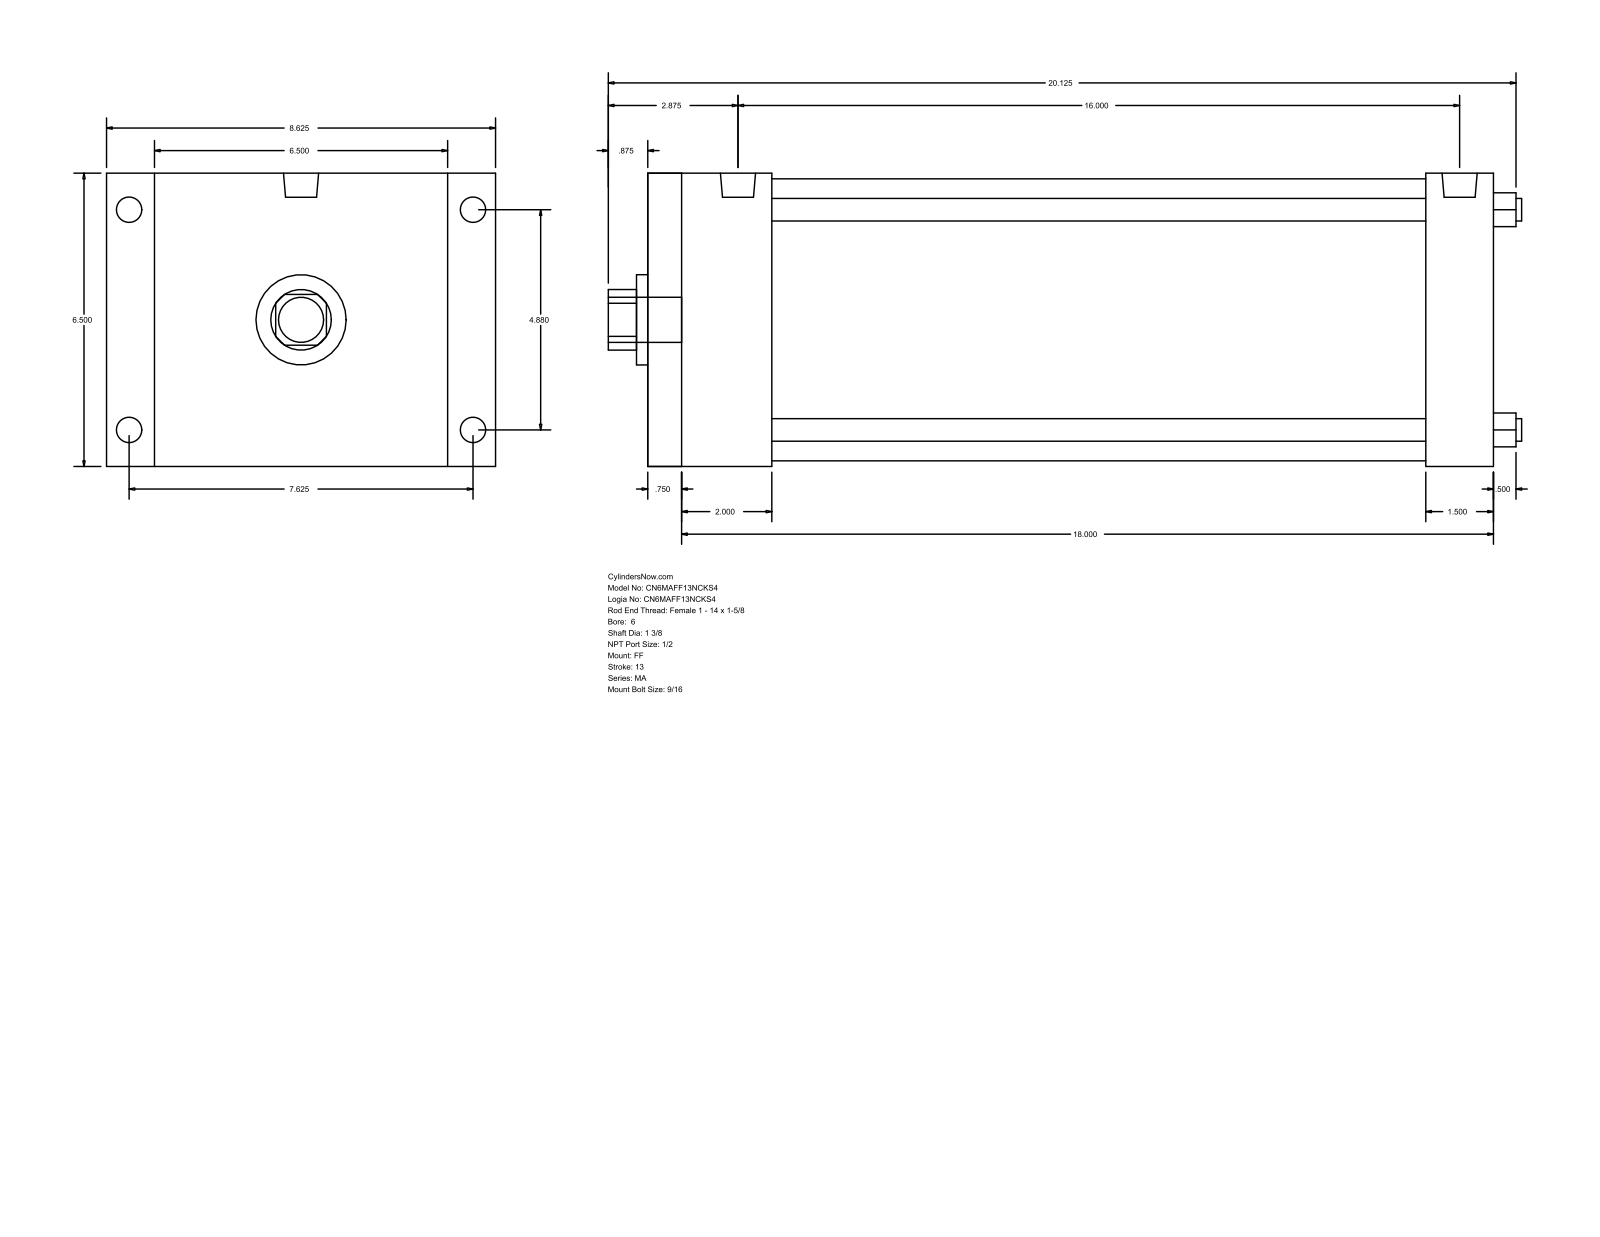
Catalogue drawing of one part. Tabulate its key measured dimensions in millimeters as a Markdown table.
| quantity | value |
| --- | --- |
| part name | MA_FF__0600_1.375 |
| STEP written by | GSSL Pune (CONFIG_CONTROL_DESIGN) |
| units | millimeters |
| bodies | 0 solids, 92 faces (64 planar, 28 cylindrical, 0 other) |
| overall size | 514.35 × 219.07 × 165.1 |
| round holes (diameter × count) | 12.7 × 4, 34.92 × 1, 50.8 × 1, 158.75 × 1 |
| round bosses / shafts (diameter × count) | 17.46 × 4, 14.29 × 4, 19.77 × 2, 25.4 × 1 |
| partial cylindrical surfaces (radius × count) | 17.06 × 1 |
| main face-to-face distances | 165.1, 476.25, 15.87, 460.38, 50.8, 422.28, 38.1, 66.67, 409.58, 438.15 |
| hole center spacings | 87.65, 123.96, 175.31 |
